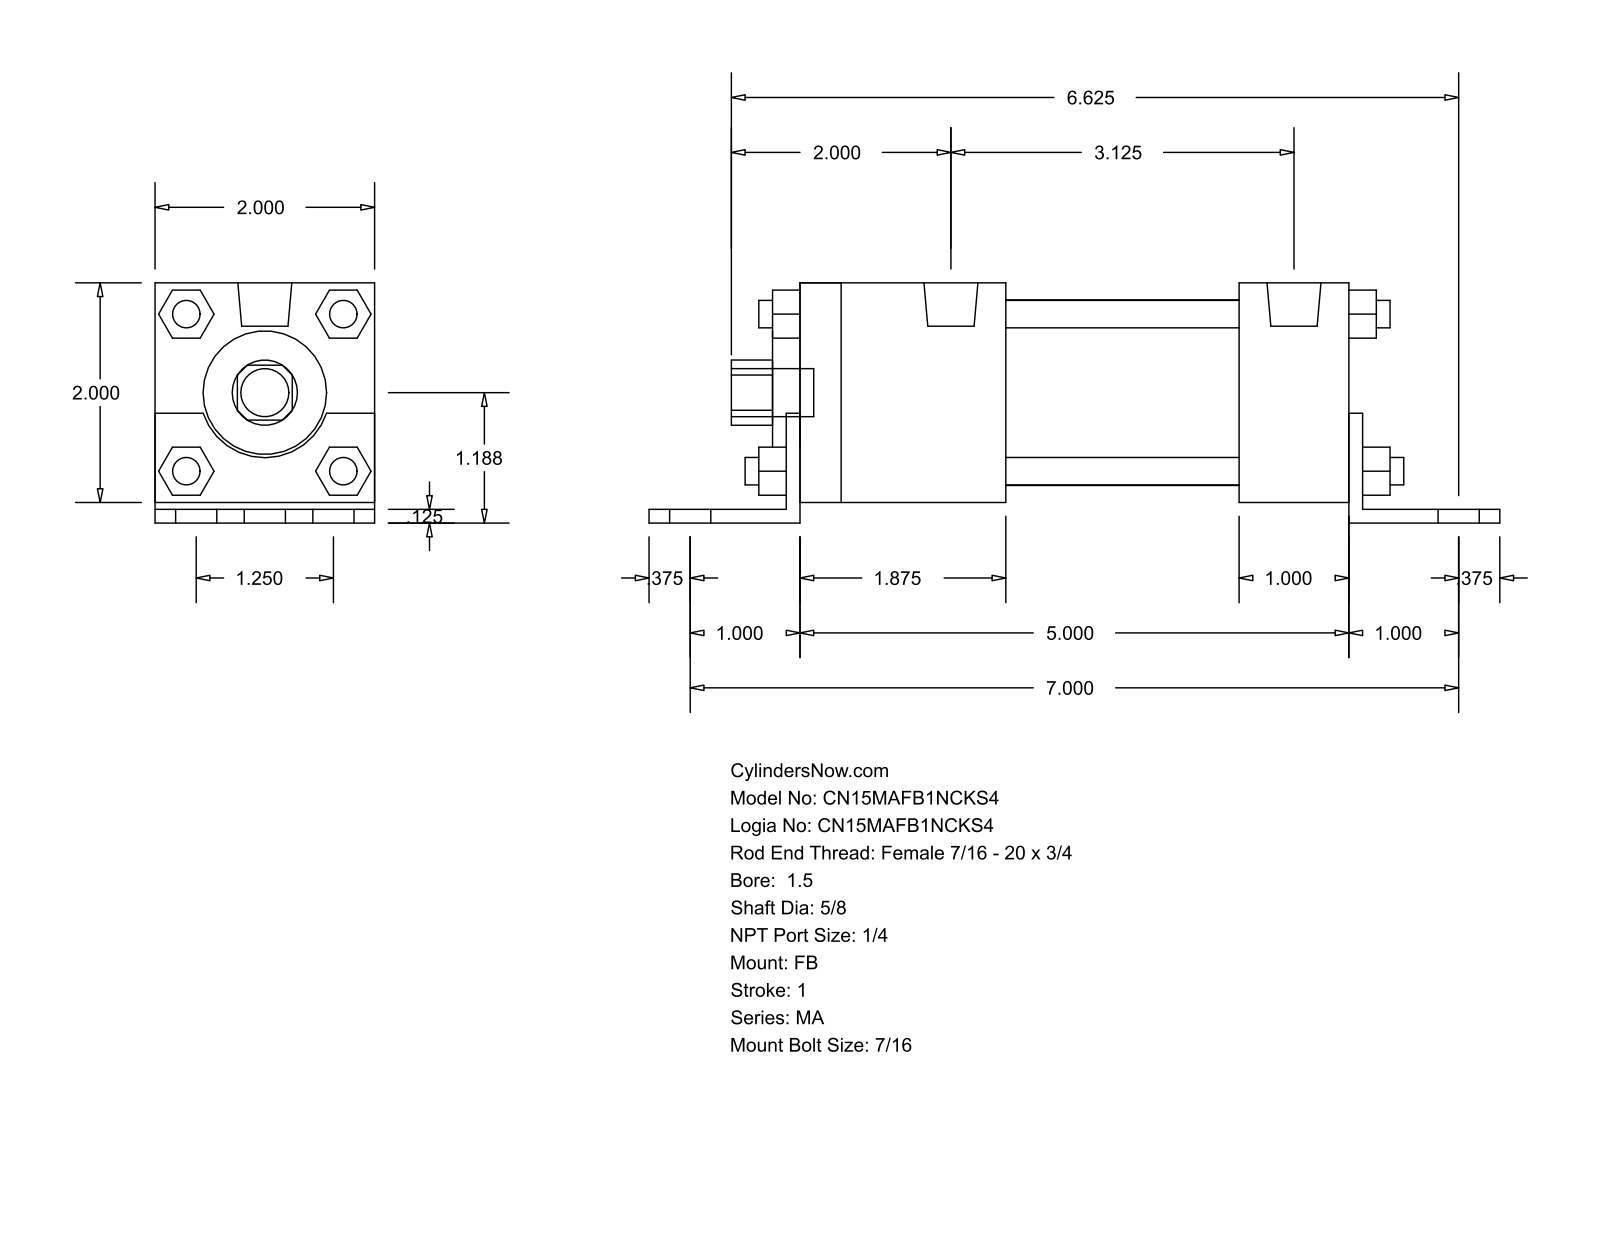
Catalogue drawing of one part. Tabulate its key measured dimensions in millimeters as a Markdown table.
| quantity | value |
| --- | --- |
| part name | MA_FB__0150_0.625 |
| STEP written by | GSSL Pune (CONFIG_CONTROL_DESIGN) |
| units | millimeters |
| bodies | 0 solids, 140 faces (105 planar, 35 cylindrical, 0 other) |
| overall size | 196.85 × 55.56 × 50.8 |
| round holes (diameter × count) | 15.88 × 1, 28.57 × 1, 42.93 × 1 |
| round bosses / shafts (diameter × count) | 11.11 × 7, 7.94 × 4, 6.35 × 4, 12.49 × 2 |
| partial cylindrical surfaces (radius × count) | 7.54 × 1, 15.05 × 1 |
| main face-to-face distances | 50.8, 3.17, 4.76, 55.56, 1.59, 52.39, 53.97, 133.35, 6.35, 127 |
